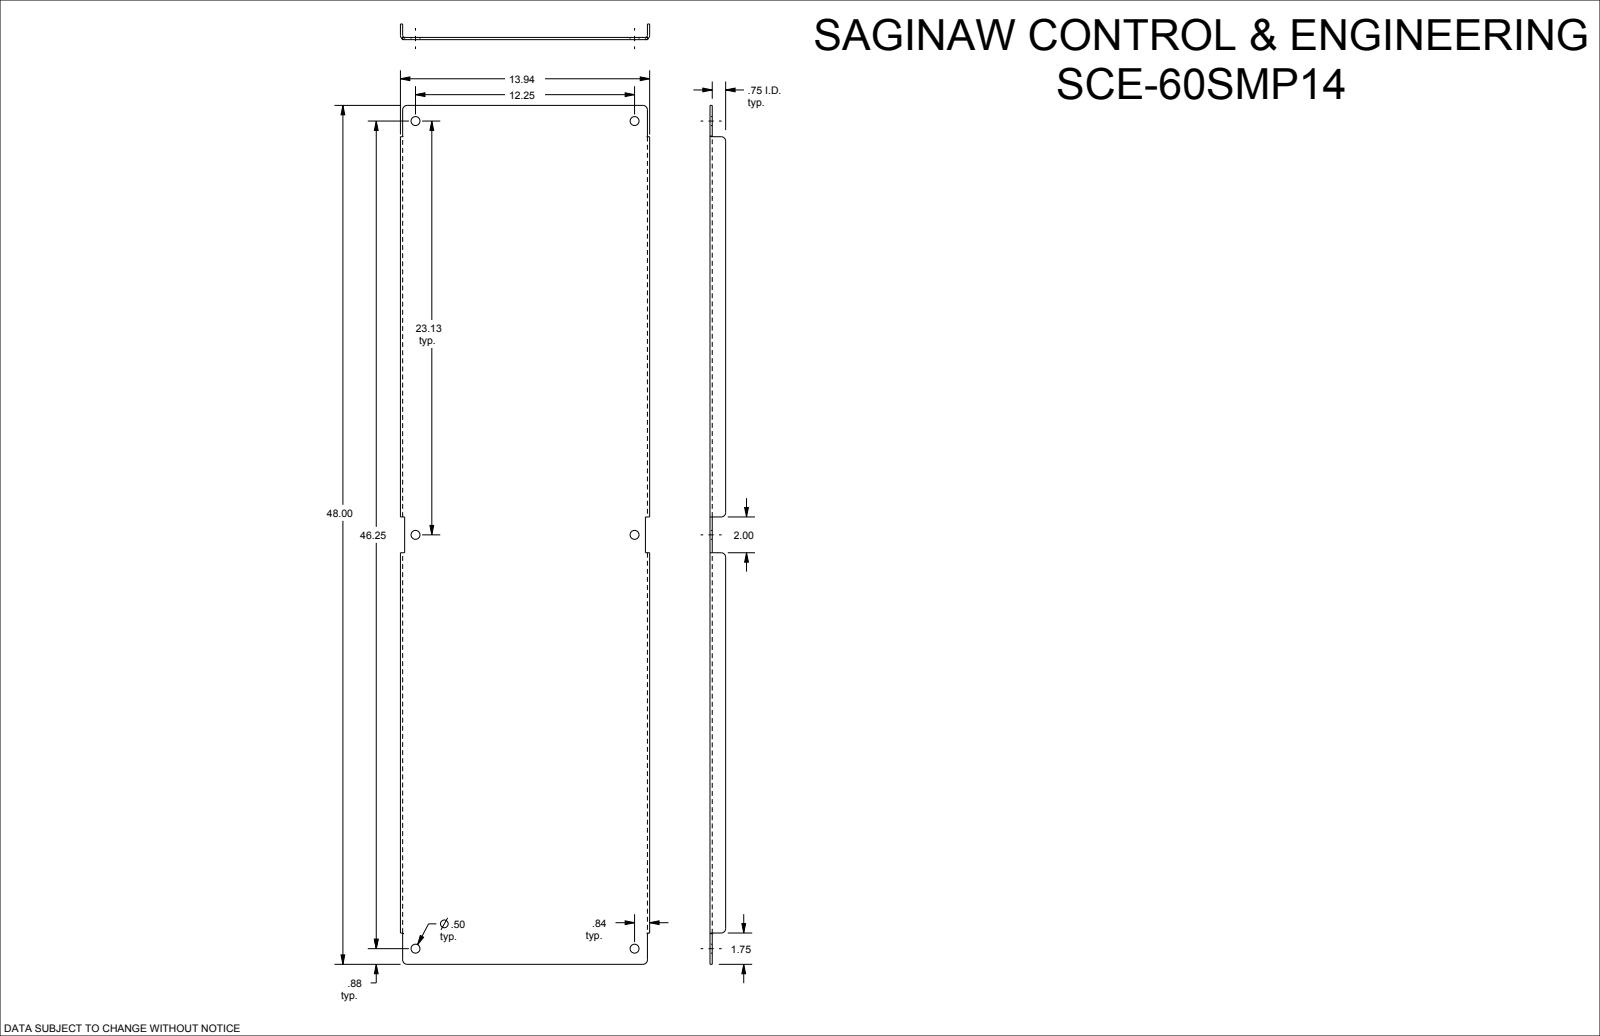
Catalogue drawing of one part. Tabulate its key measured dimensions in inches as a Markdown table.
| quantity | value |
| --- | --- |
| part name | SCE-60SMP14 |
| STEP written by | SolidWorks 2019 (CONFIG_CONTROL_DESIGN) |
| units | inches |
| bodies | 1 solid, 68 faces (30 planar, 26 cylindrical, 12 other) |
| overall size | 48 × 13.938 × 0.875 |
| volume | 90.4 in³ |
| surface area | 1 464 in² |
| round holes (diameter × count) | 0.5 × 6 |
| partial cylindrical surfaces (radius × count) | 0.25 × 8, 0.112 × 2, 0.237 × 2 |
| main face-to-face distances | 0.125, 0.125, 13.813, 13.687, 13.938, 0.75, 0.875, 48, 0.237, 13.701 |
| hole center spacings | 23.125, 26.169, 12.25, 46.25, 47.845 |
